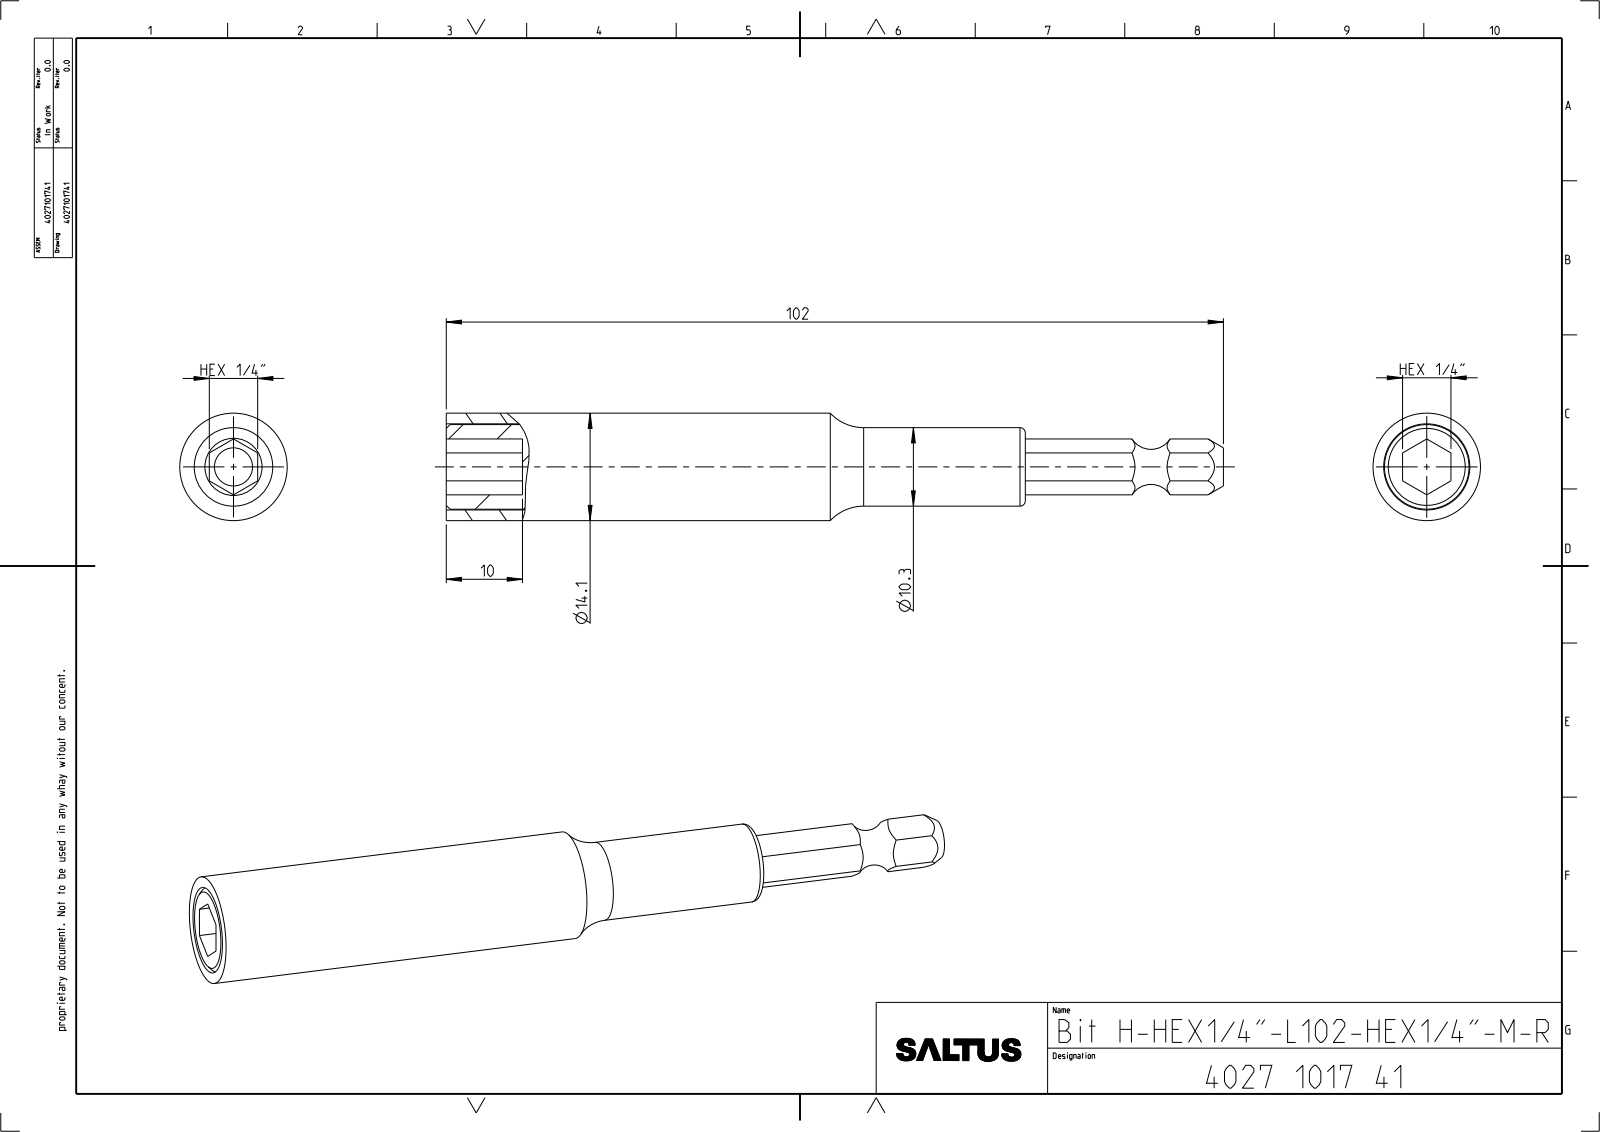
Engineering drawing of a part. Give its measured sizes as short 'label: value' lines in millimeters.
name: 4027911209; 4027299491; 4027101741_ASM
written by: CREO PARAMETRIC BY PTC INC, 2022414 (CONFIG_CONTROL_DESIGN)
unit: mm
bodies: 2 solids, 63 faces (23 planar, 18 cylindrical, 22 other)
size: 102 × 14.1 × 14.1
volume: 9 905 mm³; area: 8 747 mm²
holes: 1× ⌀7.5, 1× ⌀11.3
bosses: 1× ⌀14.1, 1× ⌀11.1, 1× ⌀10.5, 1× ⌀10.3
face distances: 6.34, 46.5, 36.5, 10, 55.5, 92, 102
